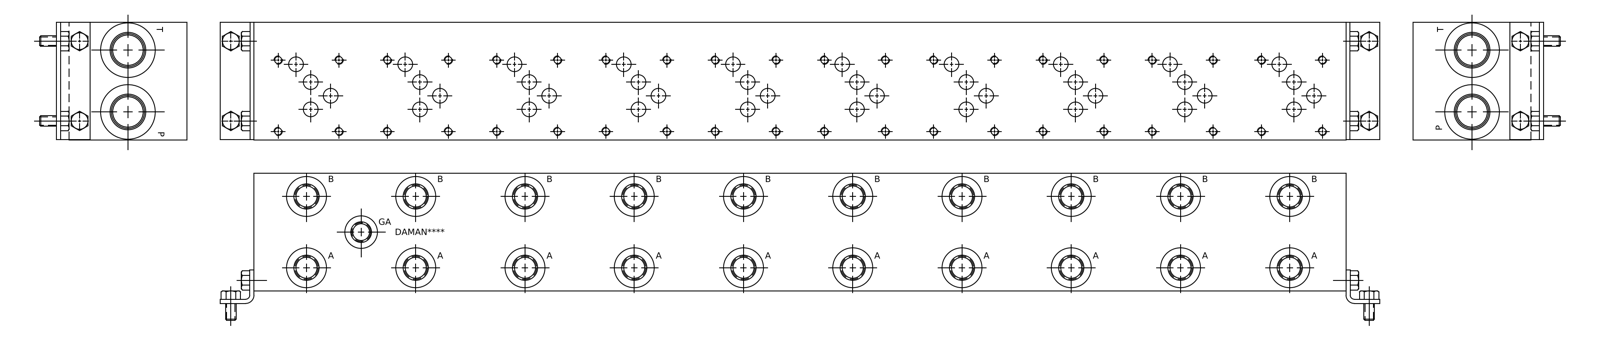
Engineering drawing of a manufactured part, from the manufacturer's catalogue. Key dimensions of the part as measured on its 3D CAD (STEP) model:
Part name (STEP PRODUCT): Part_AD05P103S_3D
STEP written by: Autodesk Inventor 2019 (AUTOMOTIVE_DESIGN)
Units: millimetres
Bodies: 1 solid, 1332 faces (628 planar, 253 cylindrical, 451 other)
Overall size (bounding box): 825.5 × 88.9 × 88.9
Volume: 6 264 000 mm³ · Surface area: 373 213 mm²
Round holes (diameter × count): ⌀5.11 ×40, ⌀6.35 ×40, ⌀11.13 ×40, ⌀15.88 ×20, ⌀17.5 ×20, ⌀19.05 ×20, ⌀19.25 ×20, ⌀30.63 ×20, ⌀6.53 ×2, ⌀7.92 ×2, ⌀23.01 ×2, ⌀24.92 ×2
Main face-to-face distances: 88.9, 0.79, 88.11, 825.5, 824.71, 823.92, 15.06, 14.27, 73.84, 19.05
Hole centre spacings: 82.55, 165.1, 247.65, 253.46, 330.2, 334.58, 98.63, 173.7
